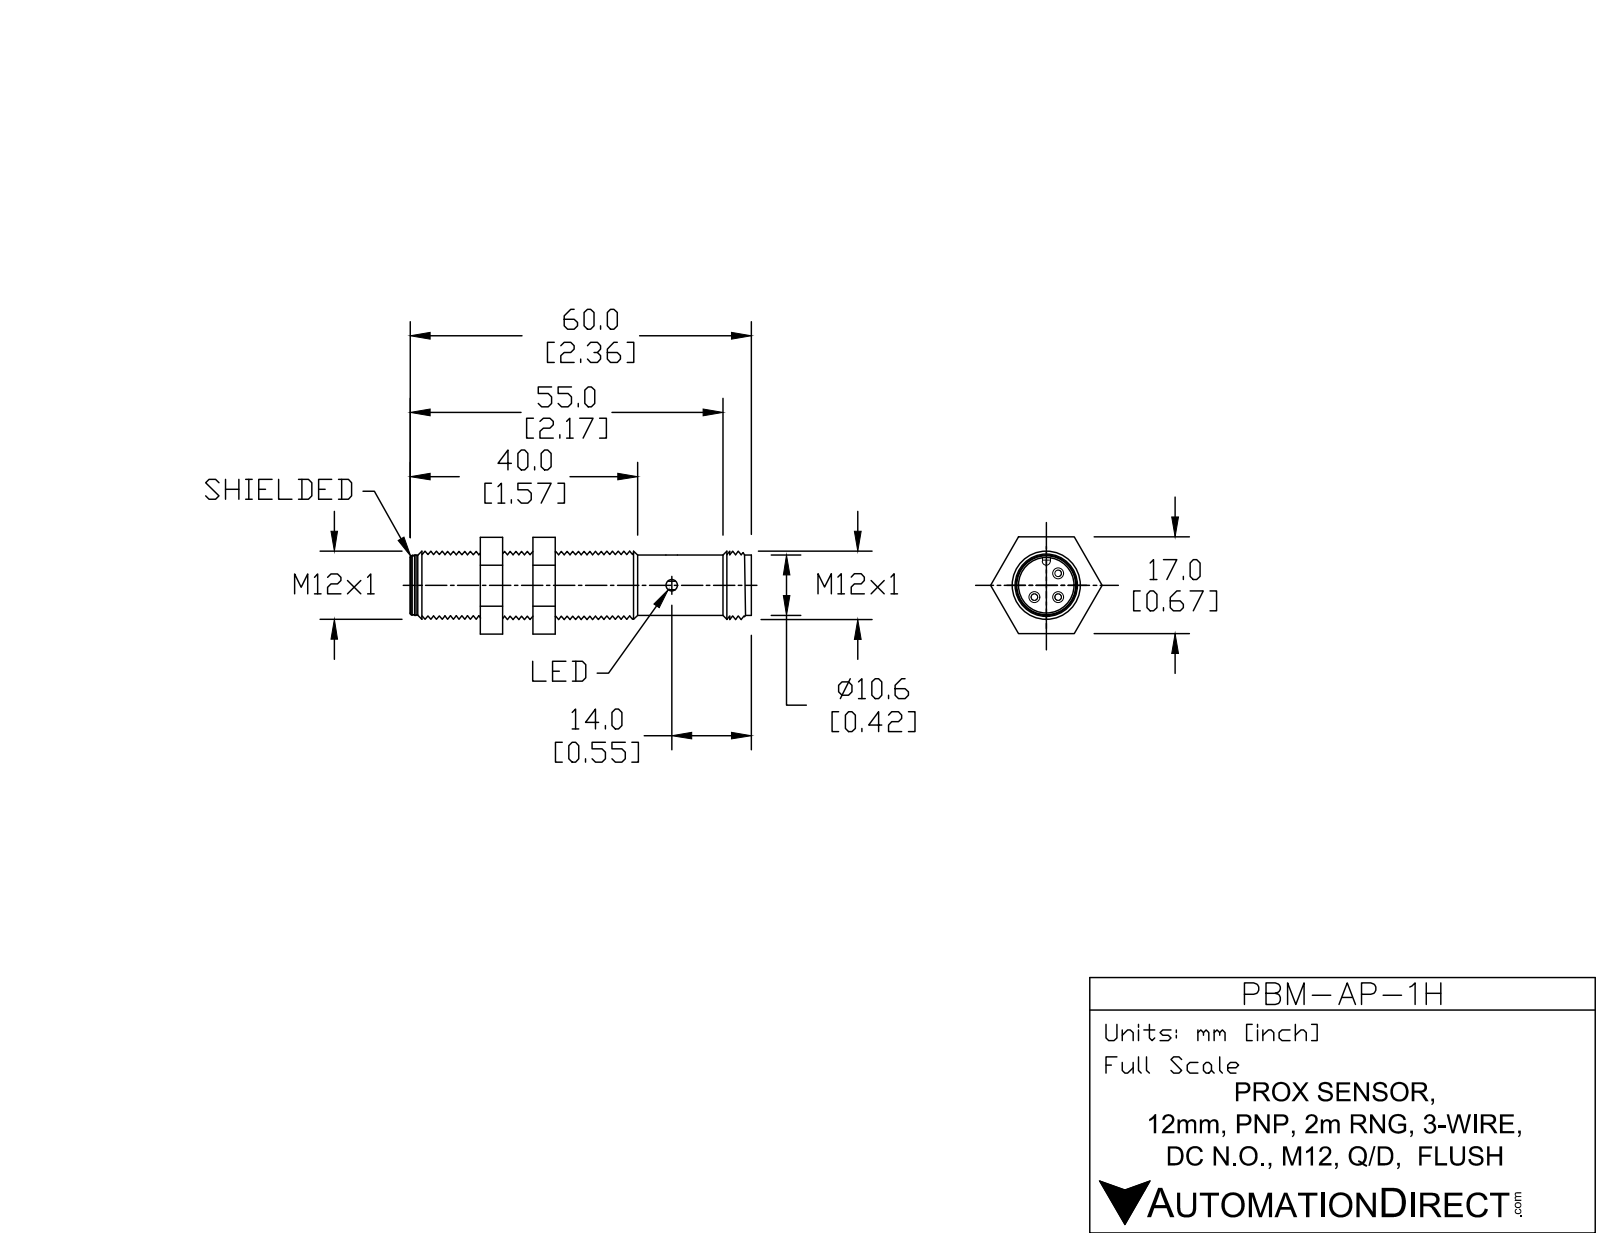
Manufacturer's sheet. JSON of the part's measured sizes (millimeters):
{"part_name": "PBM-AP-1H", "step_written_by": "SolidWorks 2011 (AUTOMOTIVE_DESIGN)", "units": "millimeters", "bodies": {"solids": 9, "faces": 66, "planar": 38, "cylindrical": 17, "other": 11}, "overall_size": [59.5, 19.63, 17.11], "volume_mm3": 6990, "surface_area_mm2": 4988, "round_holes": [[1.5, 1], [3.5, 1], [8.4, 1], [10.25, 1], [12, 1]], "round_bosses_or_shafts": [[1, 3], [10.75, 1], [10.62, 1], [10.5, 1]], "partial_cylinders_radius": [[0.5, 1]], "face_to_face_distances": [17, 10, 4, 31.75, 27.75, 6, 27, 14, 31, 21]}
